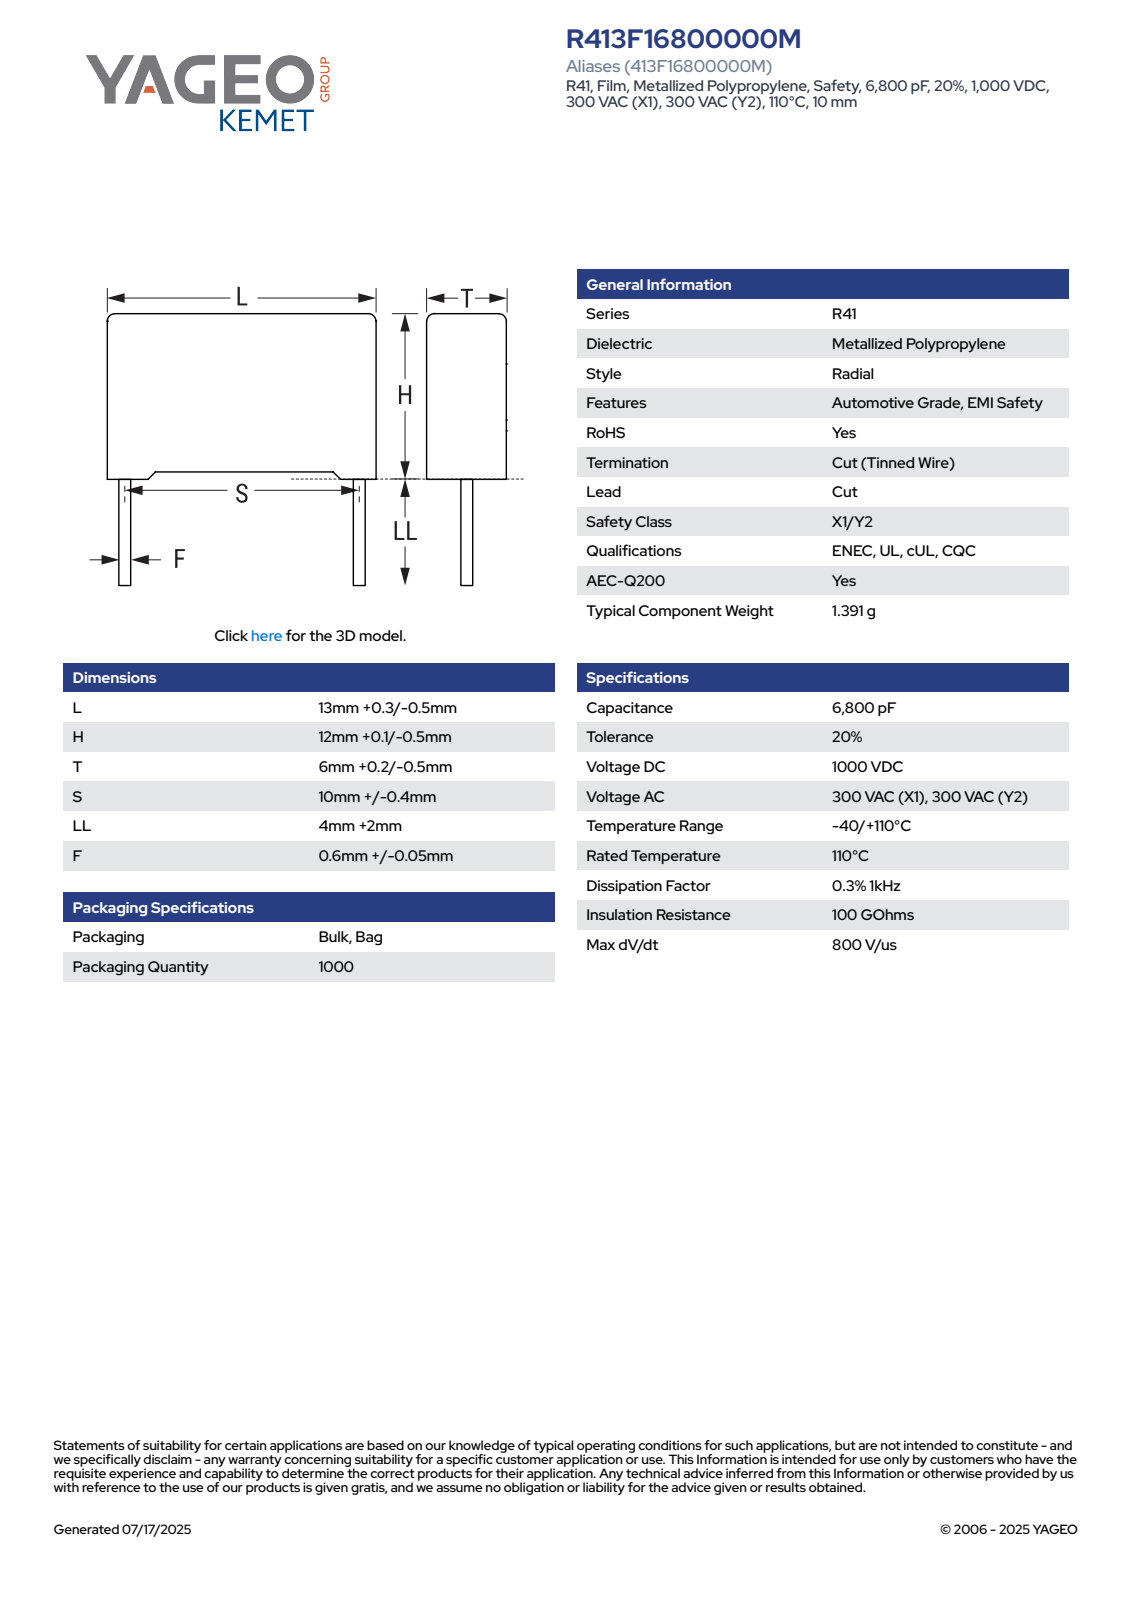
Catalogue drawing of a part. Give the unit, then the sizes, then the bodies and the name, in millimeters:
Units: millimetres
Overall size (bounding box): 18.1 × 13.3 × 6.21
Round bosses / shafts (diameter × count): ⌀0.65 ×2
Partial cylindrical surfaces — rounded edges, fillets, slot ends (radius × count): R0.5 ×4
Main face-to-face distances: 6.2, 13.3, 11.35, 0.44, 5.76, 0.75, 12.1, 12.86, 5.32, 0.42
Volume: 948 mm³ · Surface area: 685 mm²
Bodies: 4 solids, 85 faces (77 planar, 8 cylindrical, 0 other)
Part name (STEP PRODUCT): CFR_RB2_13X12X6_L13.3H12.1T6.2S10LL6F0.65
STEP written by: SolidWorks 2021 (AUTOMOTIVE_DESIGN)
